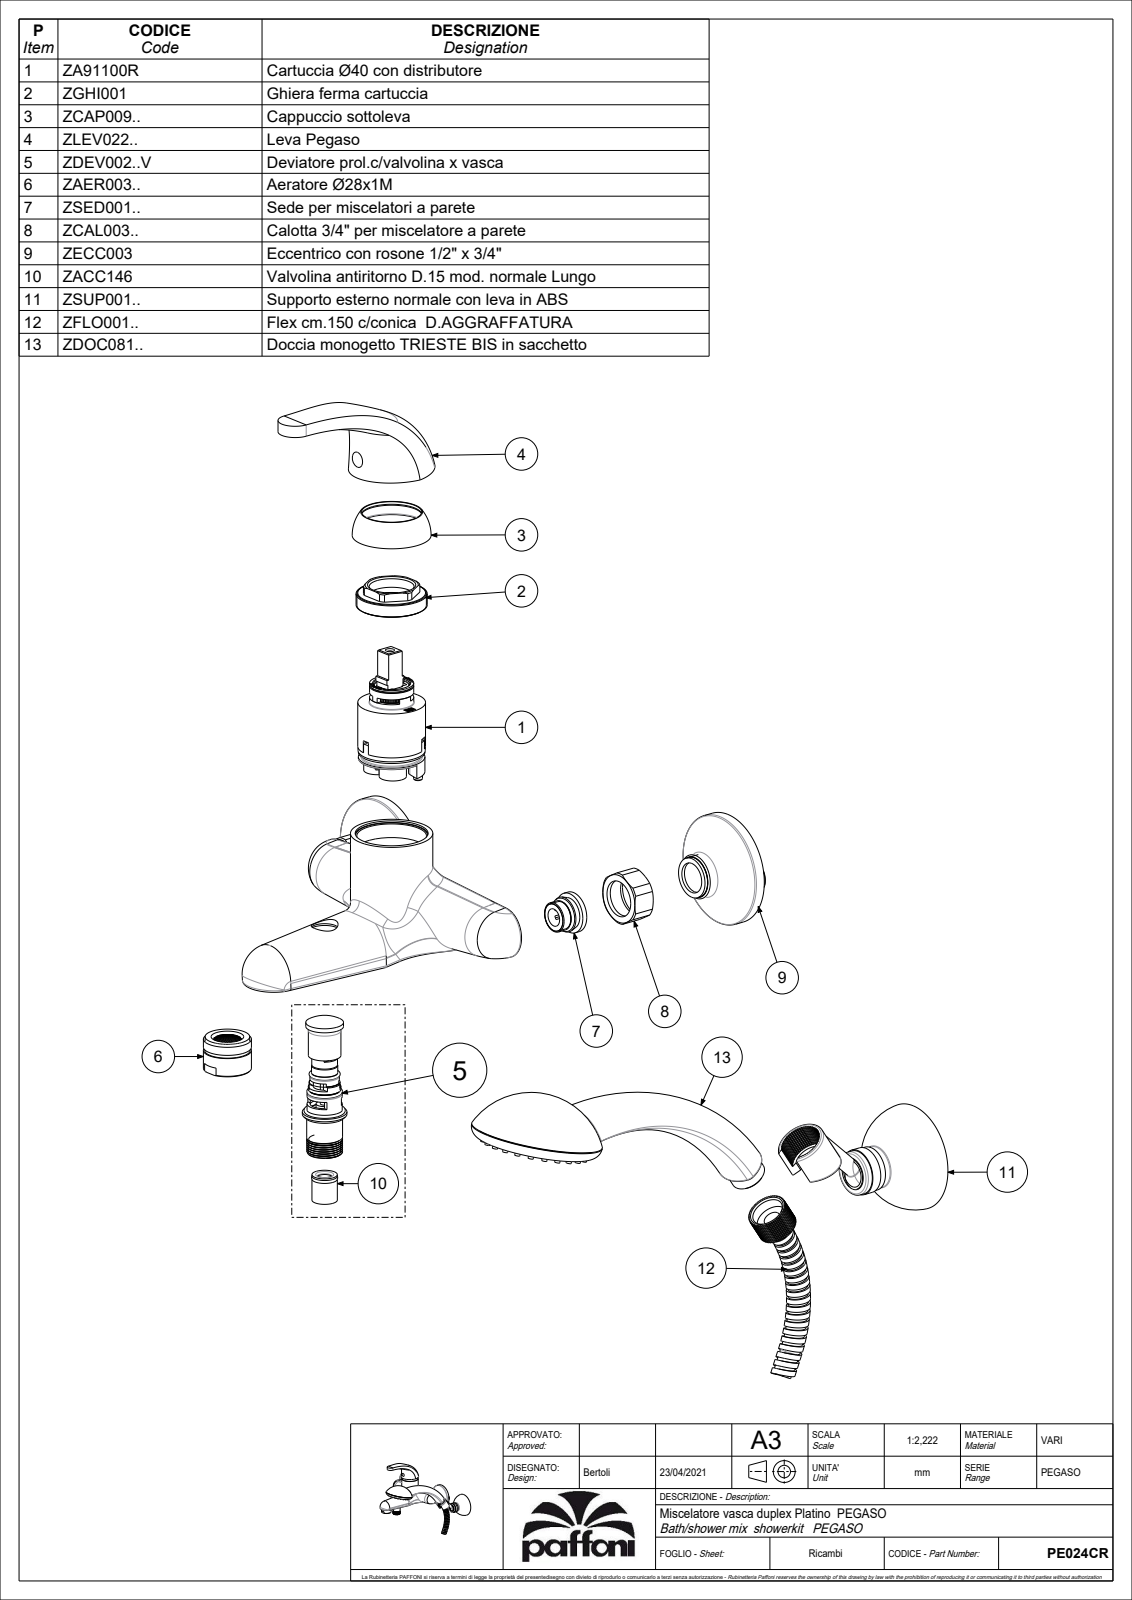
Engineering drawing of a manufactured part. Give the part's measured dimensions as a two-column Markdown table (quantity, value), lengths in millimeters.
| quantity | value |
| --- | --- |
| part name | PE024CR_SW0001 |
| STEP written by | CREO PARAMETRIC BY PTC INC, 2022124 (CONFIG_CONTROL_DESIGN) |
| units | millimeters |
| bodies | 4 solids, 1184 faces (374 planar, 258 cylindrical, 552 other) |
| overall size | 323.23 × 287.63 × 232.81 |
| volume | 758 712 mm³ |
| surface area | 155 686 mm² |
| round holes (diameter × count) | 6 × 2, 19 × 2, 21.5 × 2, 26.7 × 2, 10 × 1, 14 × 1, 15 × 1, 18 × 1, 21 × 1, 23.5 × 1 |
| round bosses / shafts (diameter × count) | 66 × 2, 26.4 × 2, 26 × 2, 21 × 2, 75.5 × 1, 48 × 1, 29 × 1, 28 × 1 |
| partial cylindrical surfaces (radius × count) | 1 × 8, 3.65 × 2, 3.8 × 2, 15.5 × 2, 15.89 × 2, 16.04 × 2, 16.27 × 2, 16.42 × 2 |
| main face-to-face distances | 34, 33.97, 34.5, 0.5, 34.47, 29, 20.5, 10.5, 1.5, 86 |
| hole center spacings | 98.27, 100, 150, 186.16, 250 |
